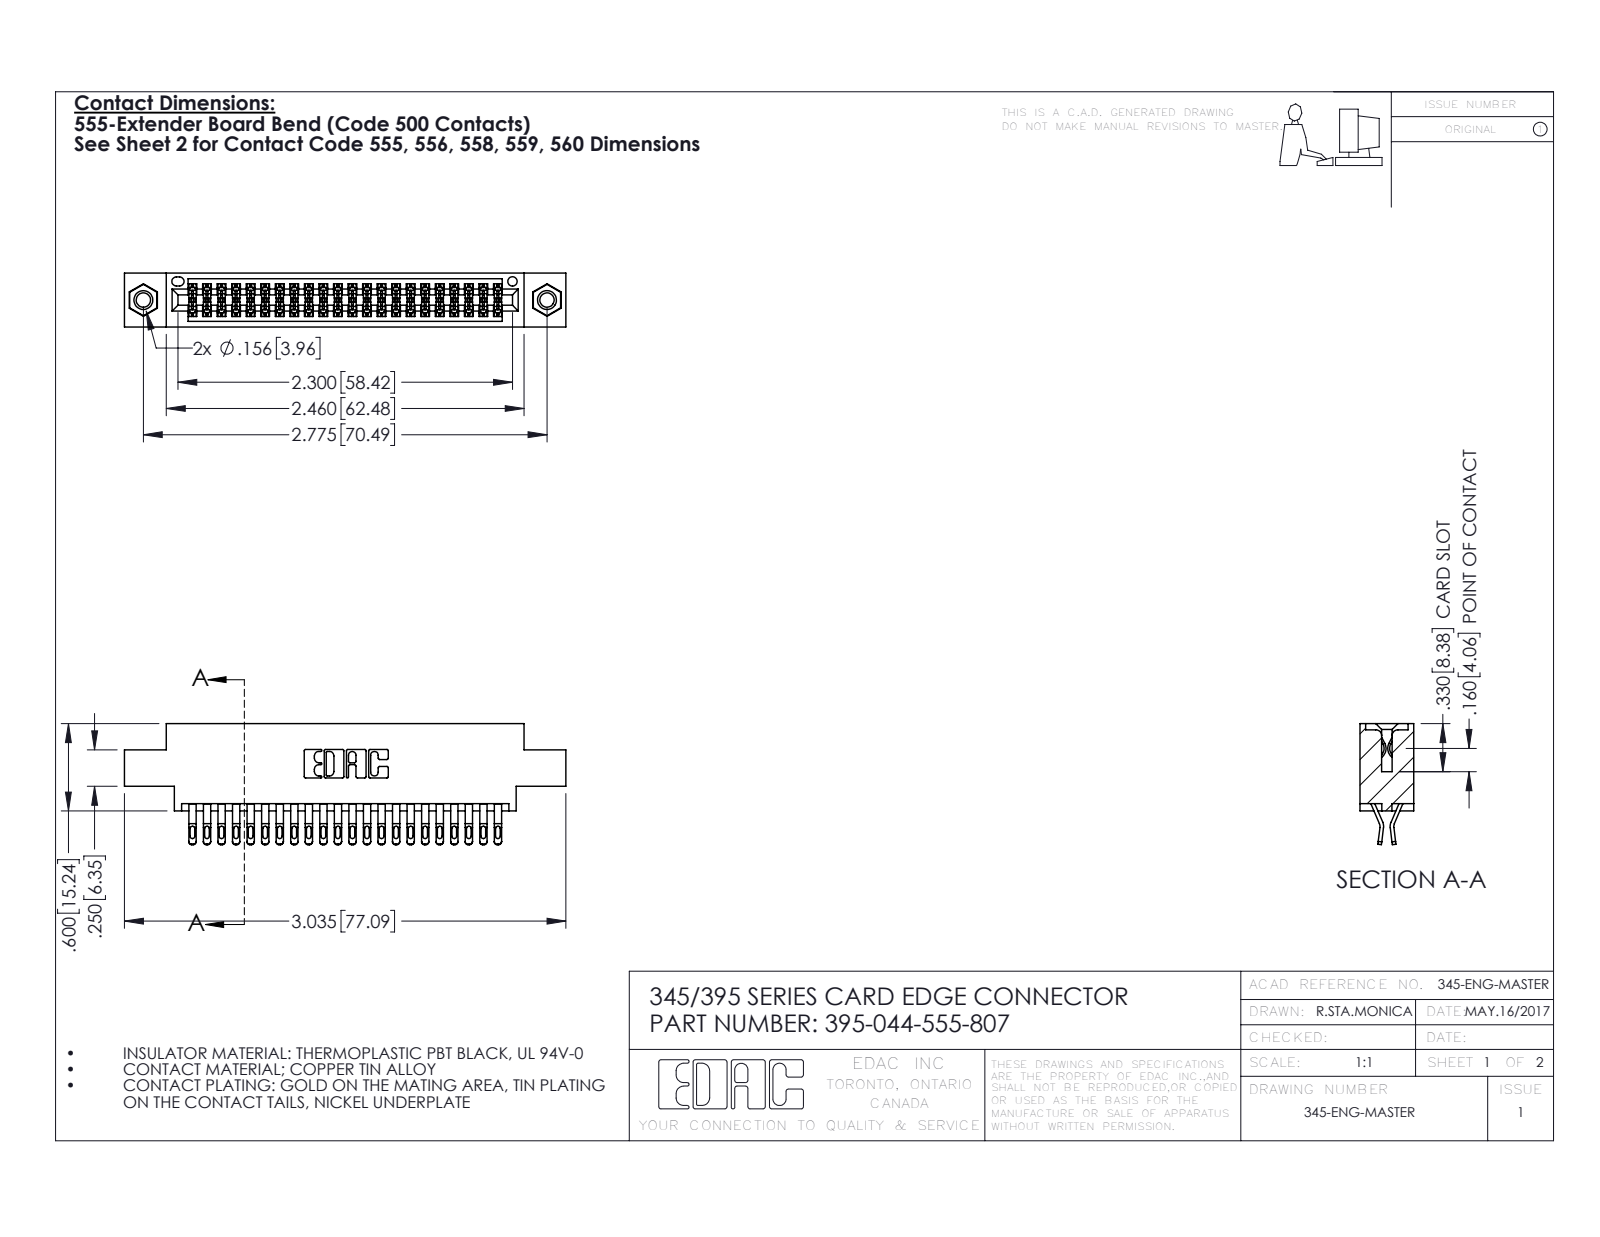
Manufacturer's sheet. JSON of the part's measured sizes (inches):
{"part_name": "395-044-555-807; 345 Part_0.170 Offset - 0.156 Dia-TI; 345-250-001_345-250-005-103; 345-292-001_555 Tail", "step_written_by": "SolidWorks 2016 (CONFIG_CONTROL_DESIGN)", "units": "inches", "bodies": {"solids": 47, "faces": 2654, "planar": 1480, "cylindrical": 1158, "other": 16}, "overall_size": [3.035, 0.832, 0.37], "volume_in3": 0.446, "surface_area_in2": 17.09, "round_holes": [[0.098, 2], [0.125, 2], [0.156, 2], [0.064, 1]], "round_bosses_or_shafts": [[0.155, 2]], "partial_cylinders_radius": [[0.016, 110], [0.02, 88], [0.006, 66], [0.01, 22], [0.007, 6], [0.031, 6], [0.026, 3], [0.01, 2]], "face_to_face_distances": [0.072, 0.298, 0.37, 0.2, 0.025, 0.098, 0.272, 0.225, 0.175, 0.149], "hole_center_spacings": [0.27, 2.541, 2.775]}
